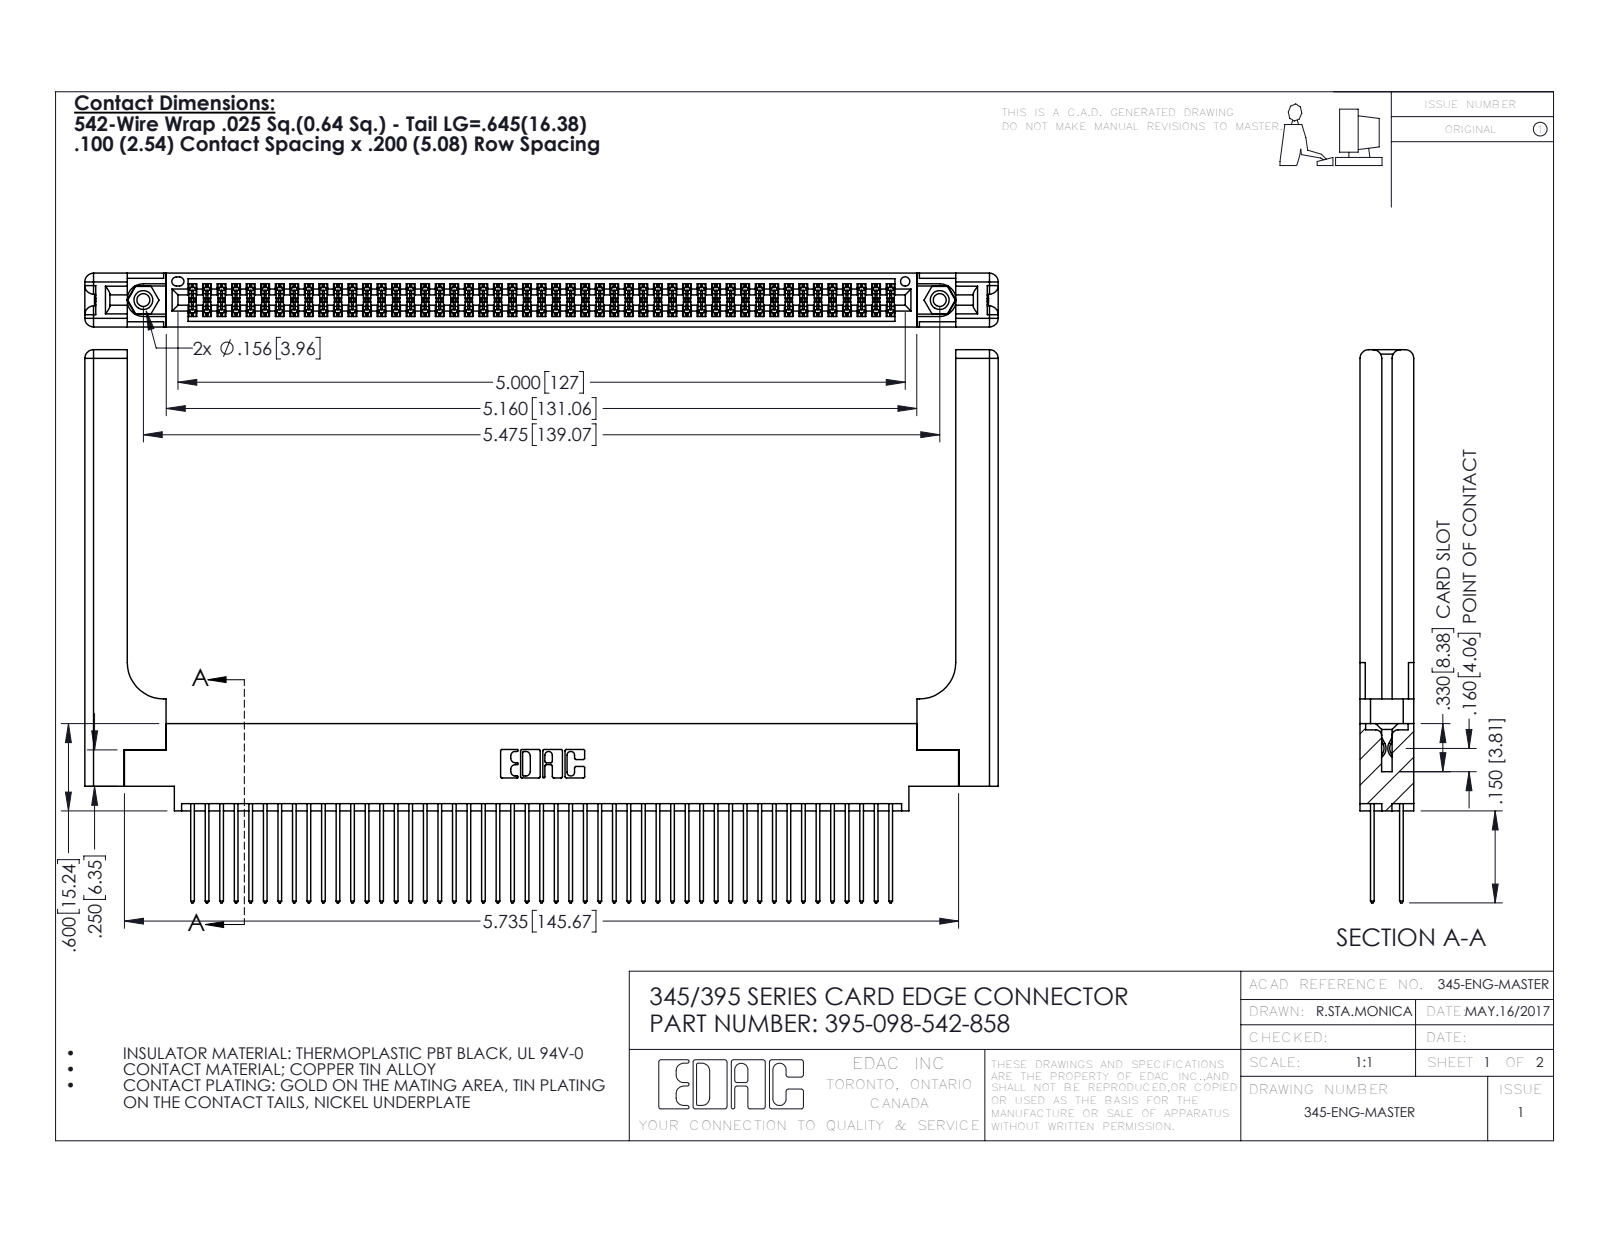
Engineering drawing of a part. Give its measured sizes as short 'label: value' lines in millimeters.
name: 345-292-001_345-293-142; 345 Part_0.170 Offset - 0.156 Dia-TH; 345-220-058_345-220-058; 345-250-001_345-250-001-102 (+1 more)
written by: SolidWorks 2016 (CONFIG_CONTROL_DESIGN)
unit: mm
bodies: 103 solids, 5286 faces (3466 planar, 1760 cylindrical, 60 other)
size: 159.5 × 96.6 × 9.4
volume: 24 380 mm³; area: 30 970 mm²
holes: 2× ⌀2.3, 2× ⌀3.2, 2× ⌀4, 1× ⌀1.6
bosses: 2× ⌀3.9
rounds: 147× R0.2, 98× R0.3, 22× R0.3, 16× R1.5, 6× R0.2, 6× R0.8, 3× R0.7, 2× R0.4
face distances: 1.8, 7.6, 9.4, 2.5, 6.9, 0.6, 5.1, 5.7, 4.4, 3.8
hole spacings: 6.9, 133.1, 139.1
